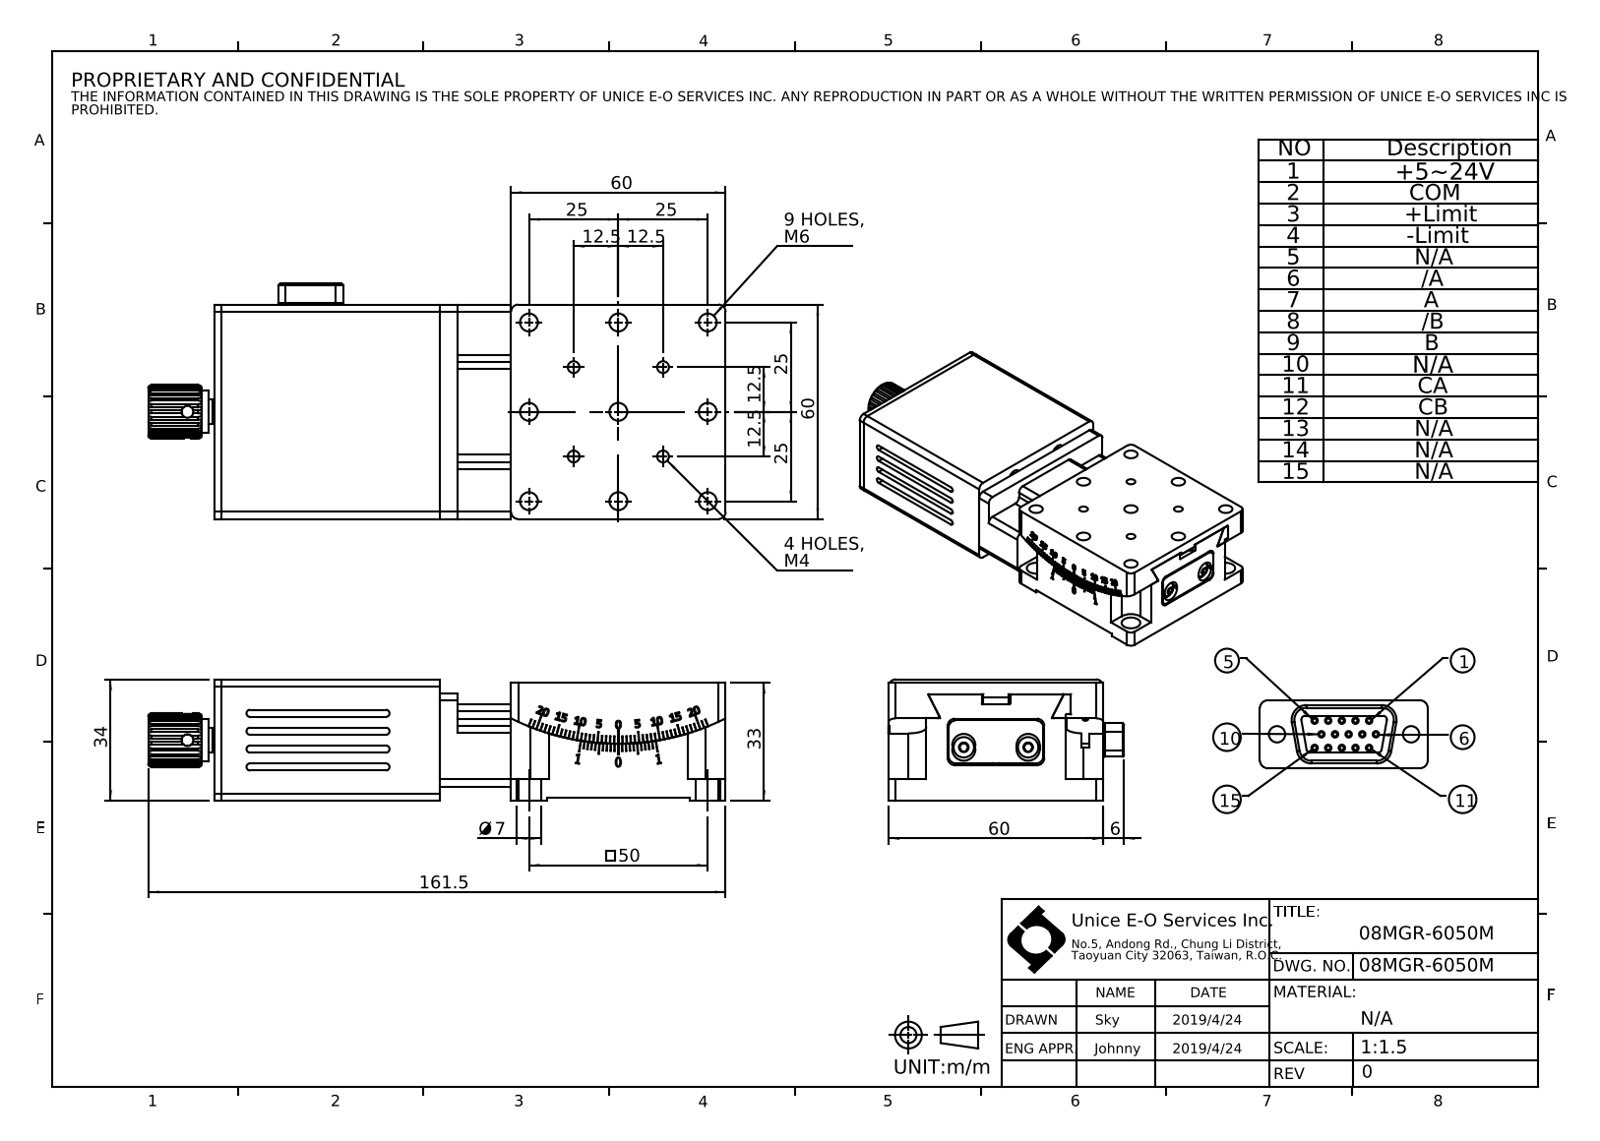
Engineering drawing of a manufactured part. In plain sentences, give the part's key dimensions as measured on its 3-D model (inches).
The part is named "08MGR-6050M". Its 3-D file was written by "SolidWorks 2016 (AUTOMOTIVE_DESIGN)". It is 0 solids with 766 faces: 342 planar, 294 cylindrical and 130 other. Overall it measures 6.358 by 2.592 by 1.339 inches. Round holes: 15 of diameter 0.031, 10 of diameter 0.063, 9 of diameter 0.197, 6 of diameter 0.13, 5 of diameter 0.098, 4 of diameter 0.094, 4 of diameter 0.217, 4 of diameter 0.276, 2 of diameter 0.089, 2 of diameter 0.12, 1 of diameter 0.906. Round bosses or shafts: 1 of diameter 0.63, 1 of diameter 0.472, 1 of diameter 0.362. Partial cylindrical surfaces (rounded edges, fillets, slot ends): 34 of radius 0.02, 30 of radius 0.079, 8 of radius 0.039, 8 of radius 0.059, 4 of radius 0.128, 4 of radius 0.197, 2 of radius 0.069, 1 of radius 0.295. The main face-to-face distances are 1.299, 0.039, 2.362, 1.339, 1.26, 0.787, 3.268, 0.118, 0.197, 0.413. The hole center spacings are 0.112, 0.984, 0.696, 1.556, 0.18, 0.2, 0.1, 0.269.
